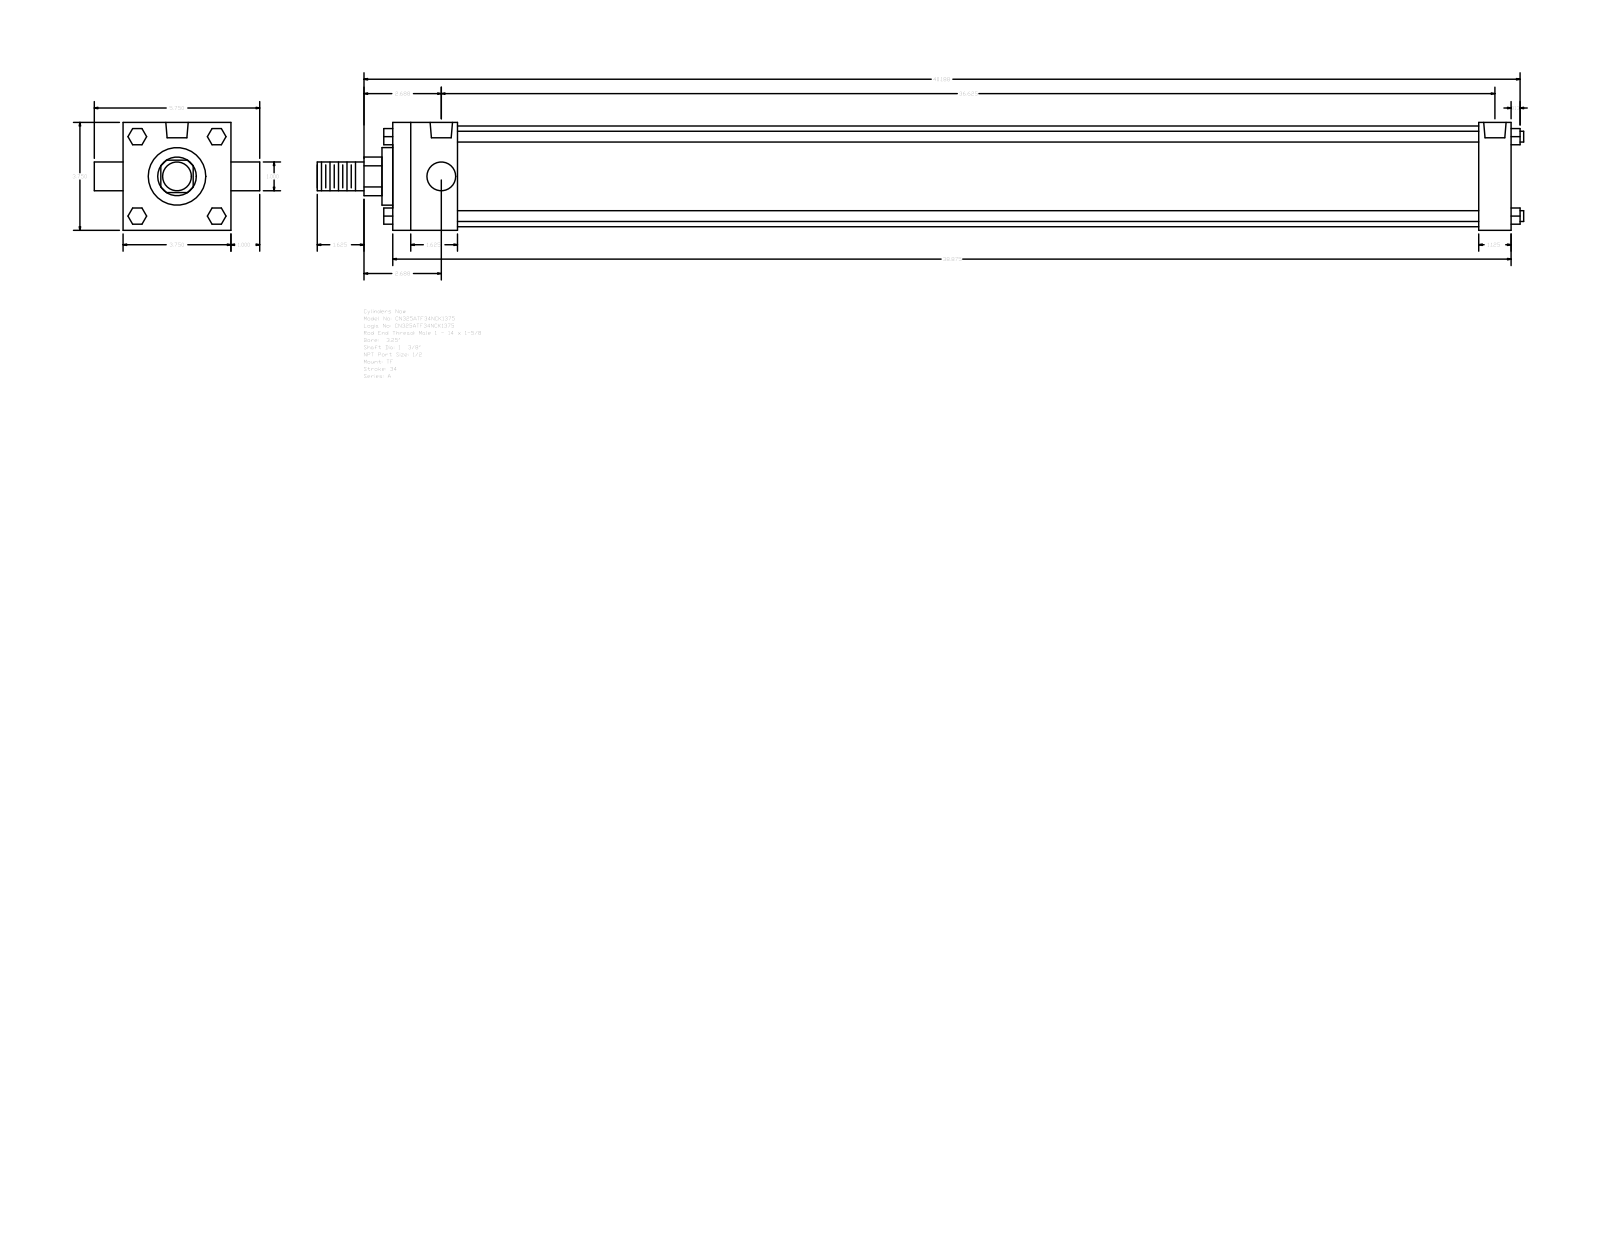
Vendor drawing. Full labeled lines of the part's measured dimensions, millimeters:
Part name (STEP PRODUCT): A_TF__0325_1.375
STEP written by: GSSL Pune (CONFIG_CONTROL_DESIGN)
Units: millimetres
Bodies: 0 solids, 120 faces (92 planar, 28 cylindrical, 0 other)
Overall size (bounding box): 1065.21 × 146.05 × 95.25
Round holes (diameter × count): ⌀8.73 ×3, ⌀19.77 ×2
Round bosses / shafts (diameter × count): ⌀9.53 ×4, ⌀25.4 ×2, ⌀88.9 ×1, ⌀50.8 ×1, ⌀34.92 ×1
Partial cylindrical surfaces — rounded edges, fillets, slot ends (radius × count): R17.06 ×1
Main face-to-face distances: 95.24, 987.43, 57.15, 28.58, 958.85, 901.7, 930.28, 66.67, 9.52, 968.37
Hole centre spacings: 3.18, 927.1, 923.92, 930.28
